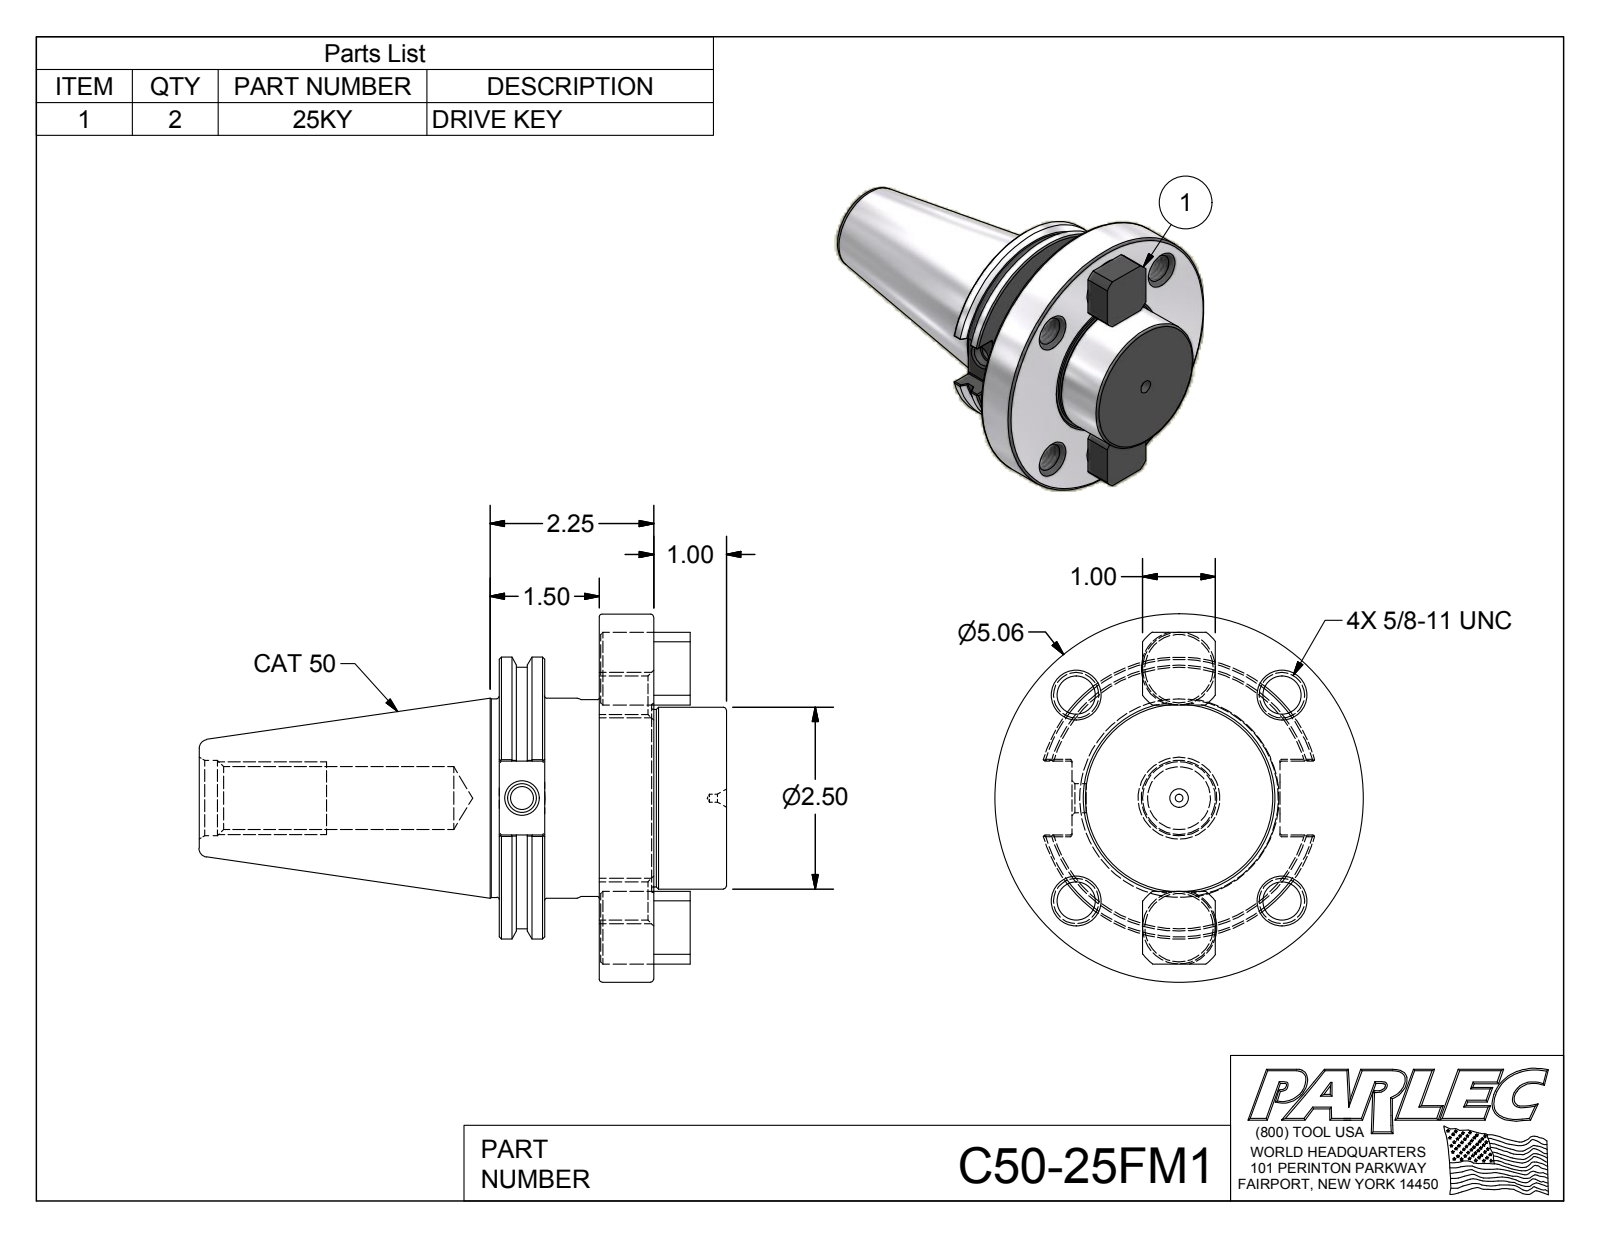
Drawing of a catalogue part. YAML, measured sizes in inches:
part_name: "C50-25FM1; C50-25FM1-1; 25KY"
step_written_by: "Autodesk Inventor 2012 (AUTOMOTIVE_DESIGN)"
units: inches
bodies: {solids: 3, faces: 143, planar: 50, cylindrical: 46, other: 47}
overall_size: [7.25, 5.061, 5.061]
volume: 44.7
surface_area: 136.9
round_holes:
  - {diameter: 0.527, count: 4}
  - {diameter: 1, count: 2}
  - {diameter: 0.109, count: 1}
  - {diameter: 0.315, count: 1}
  - {diameter: 0.399, count: 1}
  - {diameter: 0.865, count: 1}
  - {diameter: 1.038, count: 1}
round_bosses_or_shafts:
  - {diameter: 1, count: 2}
  - {diameter: 5.061, count: 1}
  - {diameter: 3.875, count: 1}
  - {diameter: 3.594, count: 1}
  - {diameter: 2.75, count: 1}
  - {diameter: 2.73, count: 1}
  - {diameter: 2.5, count: 1}
  - {diameter: 2.44, count: 1}
partial_cylinders:
  - {radius: 0.02, count: 12}
  - {radius: 0.49, count: 2}
  - {radius: 0.62, count: 2}
face_to_face_distances: [0.75, 1, 1.75, 1.375, 2.125, 3.125, 0.625, 1.5, 2.5, 0.5]
hole_center_spacings: [1.461, 2, 2.828, 3.493, 1.78, 4, 3.56]
